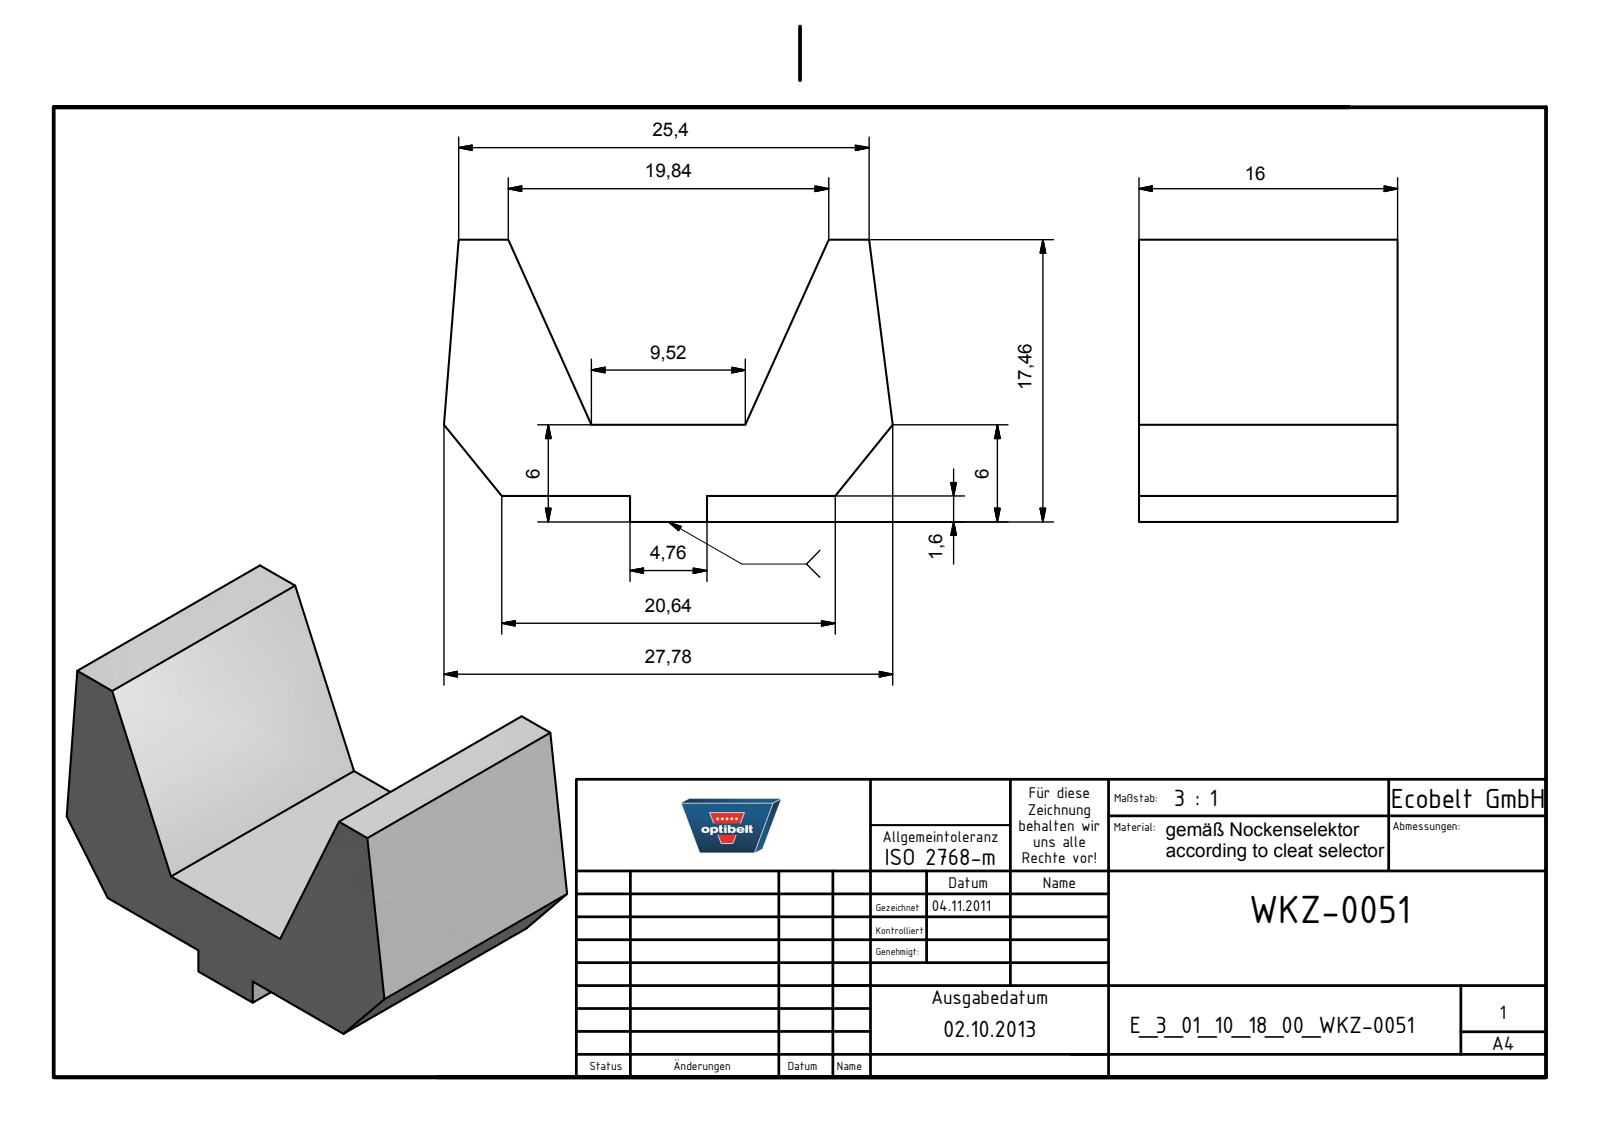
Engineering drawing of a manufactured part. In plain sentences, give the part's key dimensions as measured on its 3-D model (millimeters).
The part is named "E_3_01_10_18_00_WKZ-0051". Its 3-D file was written by "Autodesk Inventor 2025 (AUTOMOTIVE_DESIGN)". It is 1 solid with 16 faces: 16 planar, 0 cylindrical and 0 other. Overall it measures 27.78 by 17.46 by 16 millimeters. Its volume is 4 010 cubic millimeters and its surface area 2 076 square millimeters. The main face-to-face distances are 16, 4.4, 15.86, 11.46, 1.6, 6, 17.46, 4.76.
